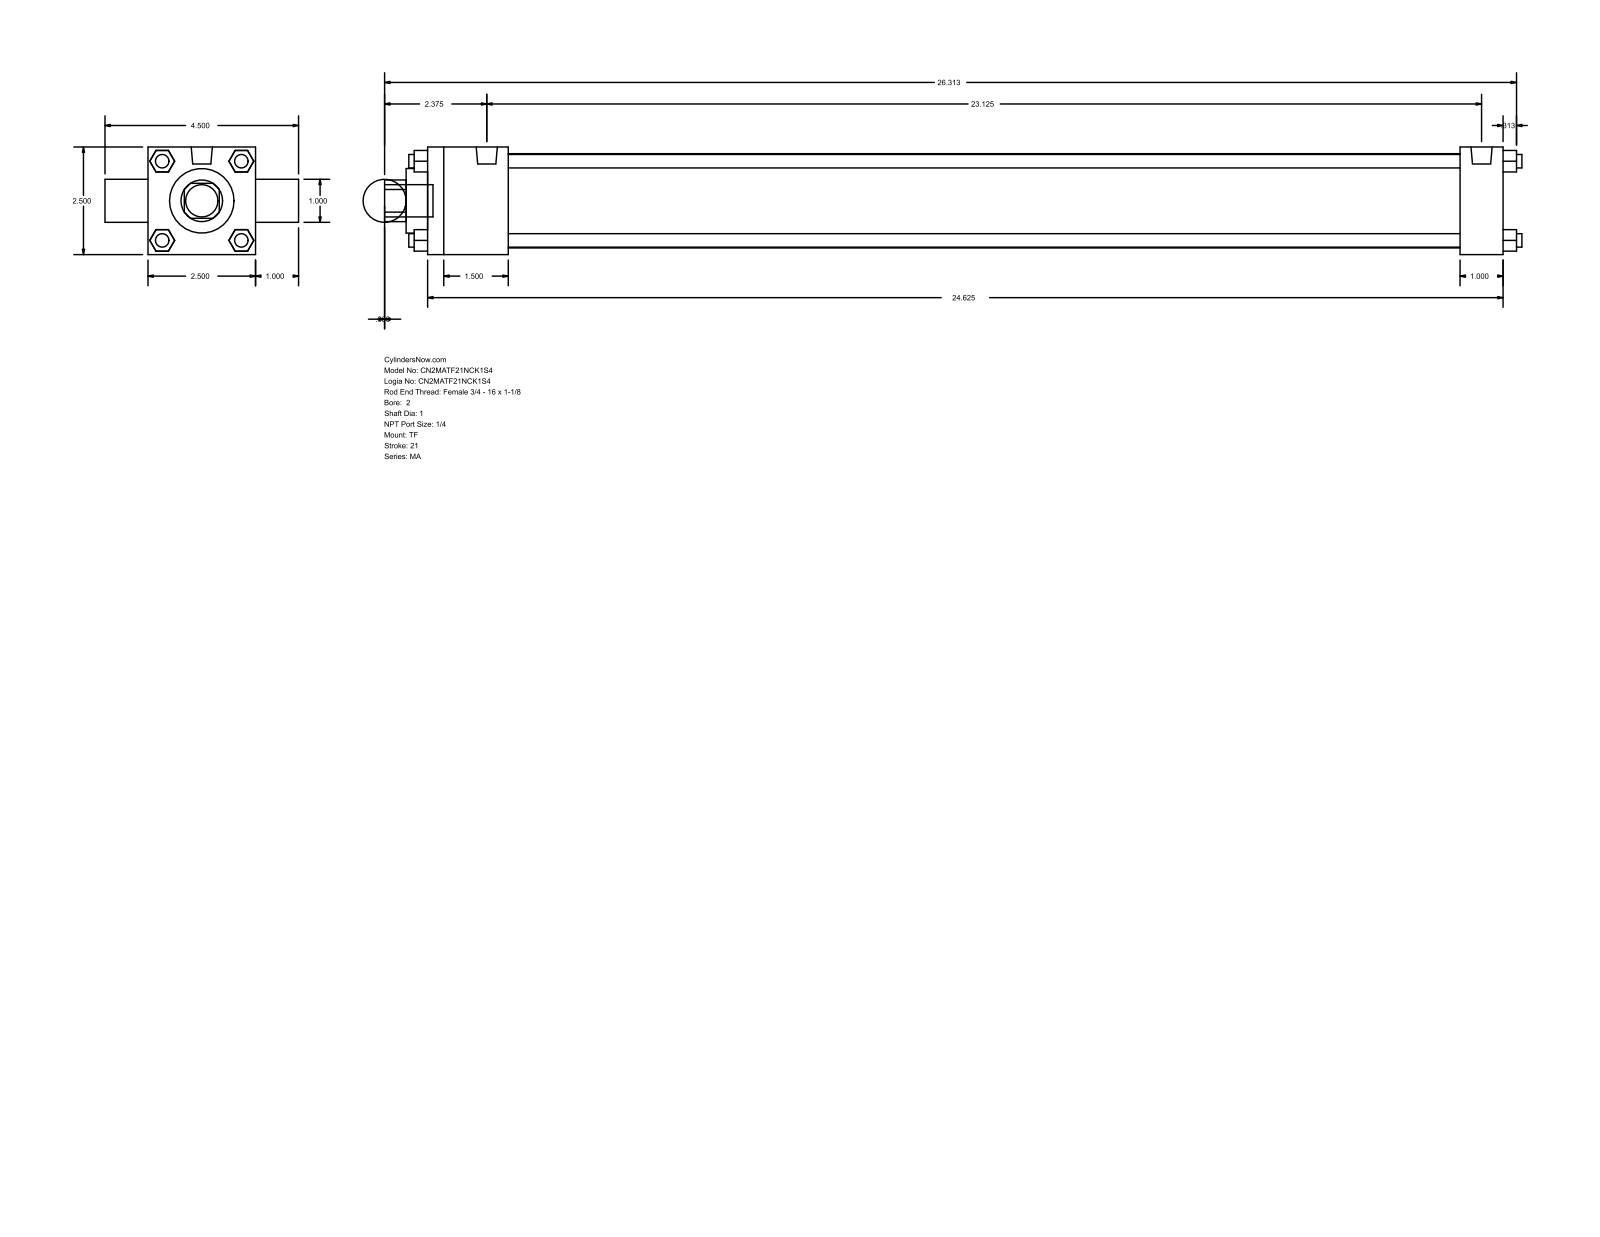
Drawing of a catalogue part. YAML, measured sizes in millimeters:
part_name: "MA_TF__0200_1"
step_written_by: "GSSL Pune (CONFIG_CONTROL_DESIGN)"
units: millimeters
bodies: {solids: 0, faces: 120, planar: 92, cylindrical: 28, other: 0}
overall_size: [671.51, 114.3, 63.5]
round_holes:
  - {diameter: 25.4, count: 2}
  - {diameter: 38.1, count: 1}
  - {diameter: 55.63, count: 1}
round_bosses_or_shafts:
  - {diameter: 7.94, count: 7}
  - {diameter: 12.49, count: 2}
  - {diameter: 19.05, count: 1}
partial_cylinders:
  - {radius: 12.29, count: 1}
face_to_face_distances: [63.5, 25.4, 635, 12.7, 47.63, 609.6, 561.97, 587.37, 88.9, 23.37]
